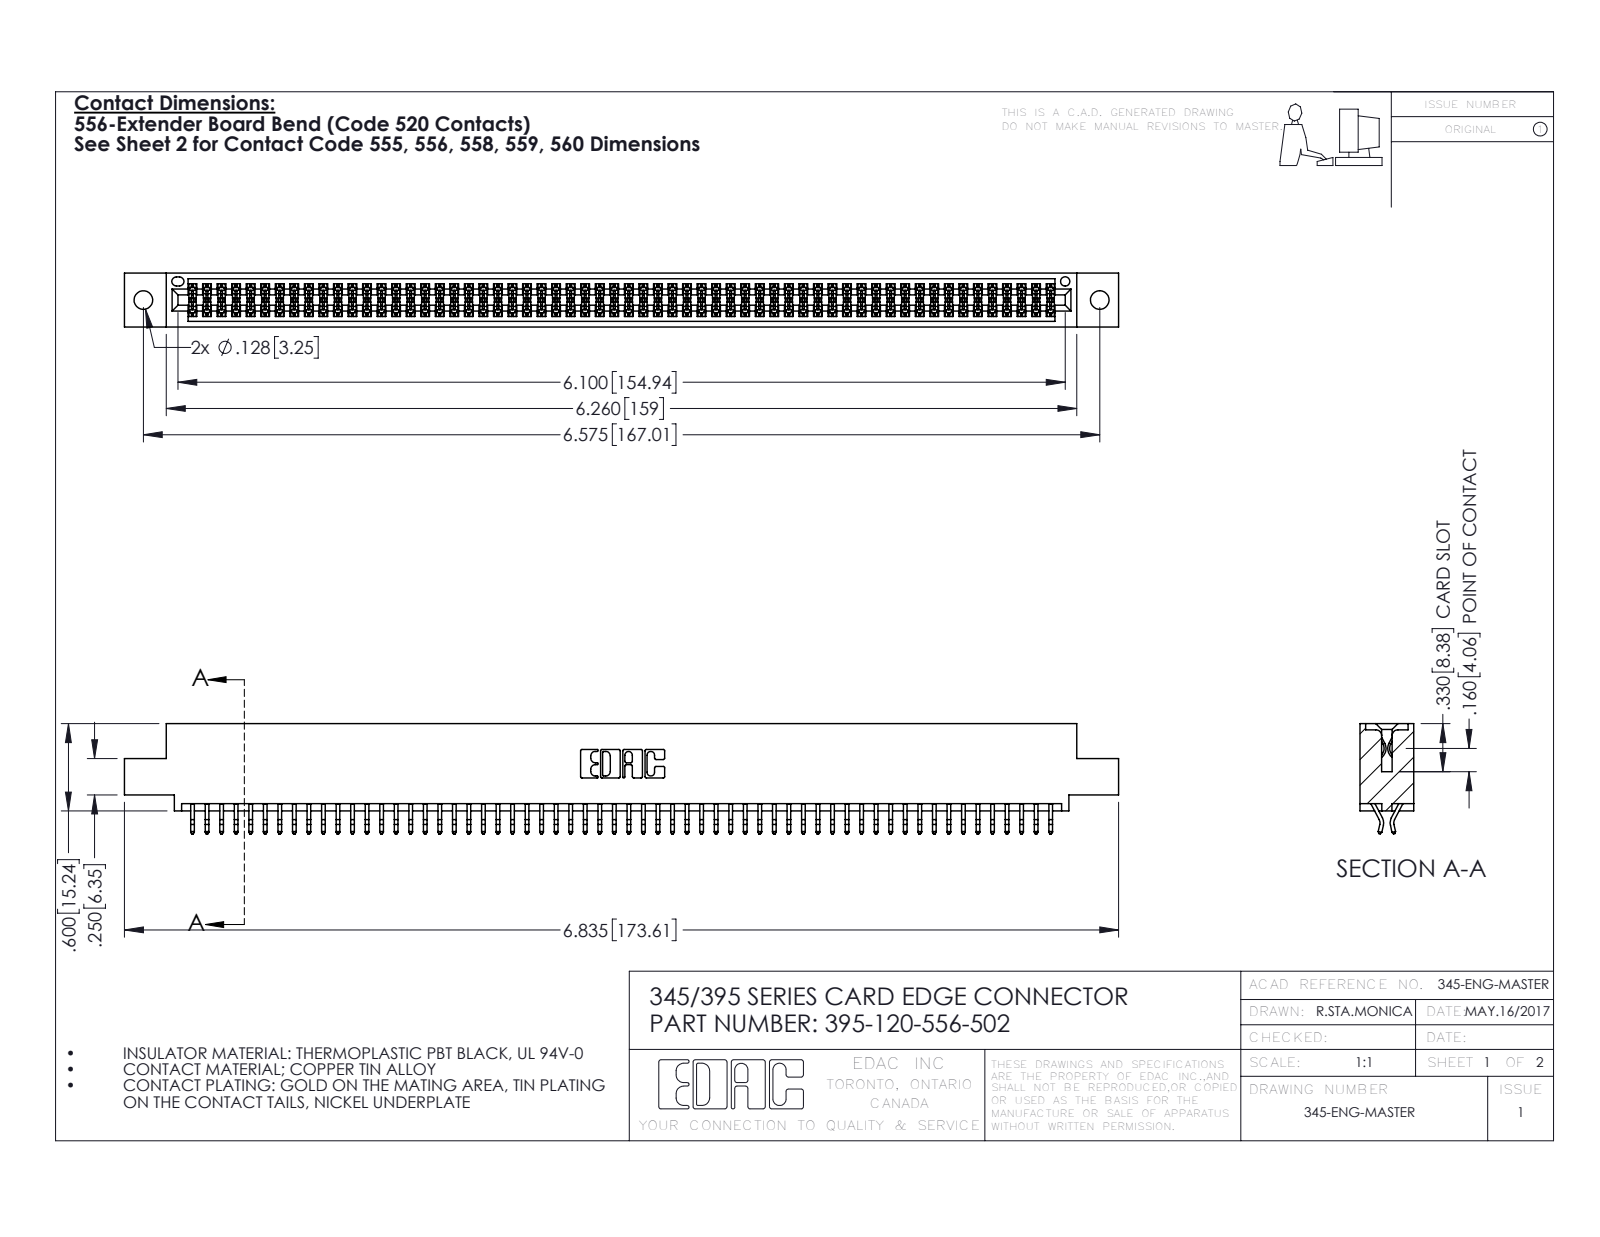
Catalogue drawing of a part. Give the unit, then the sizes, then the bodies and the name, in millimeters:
Units: millimetres
Overall size (bounding box): 173.6 × 19.2 × 9.4
Round holes (diameter × count): ⌀3.3 ×2, ⌀1.6 ×1
Partial cylindrical surfaces — rounded edges, fillets, slot ends (radius × count): R0.2 ×180, R0.3 ×22, R0.2 ×6, R0.8 ×6, R0.7 ×3, R0.3 ×2, R0.4 ×2, R0.5 ×2
Main face-to-face distances: 7.6, 1.8, 9.4, 5.1, 0.6, 2.5, 6.9, 5.7, 4.4, 3.8
Hole centre spacings: 6.9, 161, 167
Volume: 16 910 mm³ · Surface area: 25 070 mm²
Bodies: 121 solids, 6850 faces (4524 planar, 2326 cylindrical, 0 other)
Part name (STEP PRODUCT): 345-292-001_556 Tail; 395-120-556-502; 345 Part_0.110 Offset - 0.128 Dia
STEP written by: SolidWorks 2016 (CONFIG_CONTROL_DESIGN)
